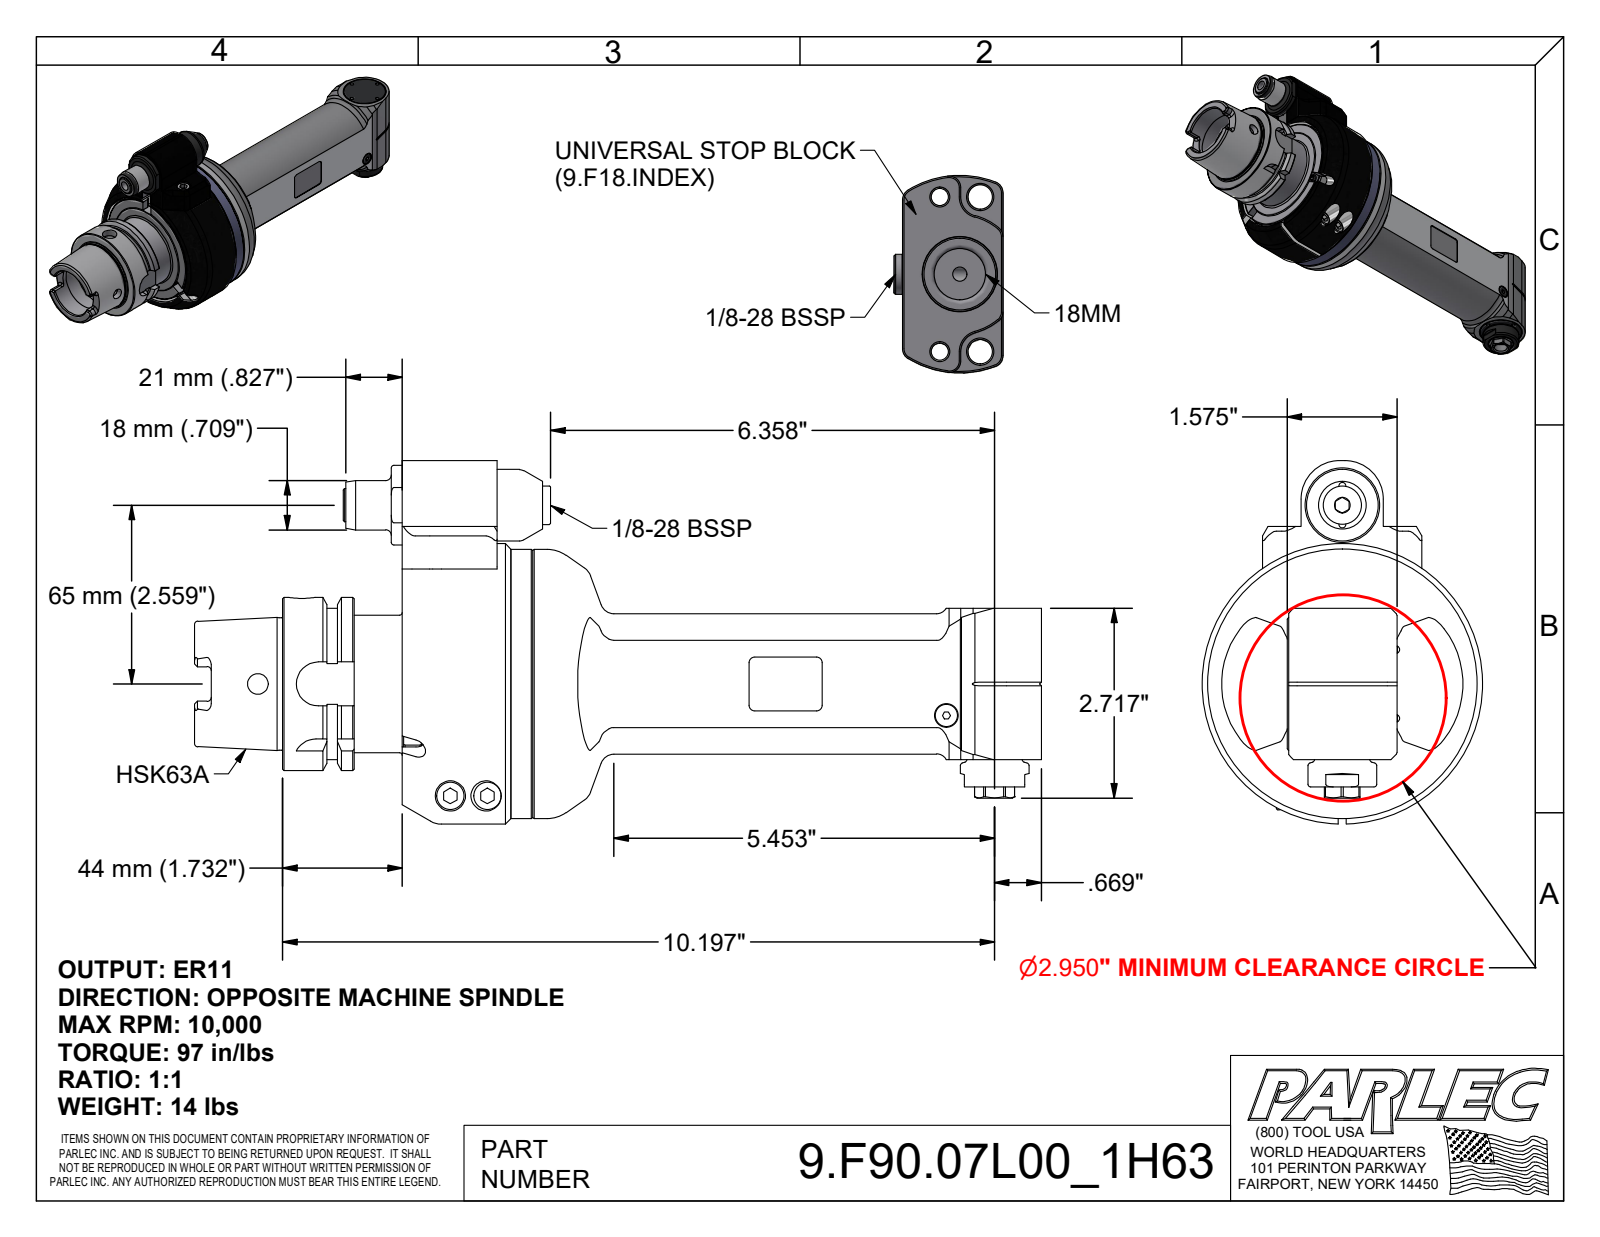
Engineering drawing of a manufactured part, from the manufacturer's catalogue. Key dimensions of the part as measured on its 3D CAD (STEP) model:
Part name (STEP PRODUCT): 9.F90.07L00-1H63; 9_GA1_566_2_1_H63; 9FL1ATC; 9HSK631ATC (+4 more)
STEP written by: Autodesk Inventor 2022 (AUTOMOTIVE_DESIGN)
Units: inches
Bodies: 5 solids, 557 faces (264 planar, 138 cylindrical, 155 other)
Overall size (bounding box): 12.126 × 5.206 × 4.016
Volume: 59.31 in³ · Surface area: 223.5 in²
Round holes (diameter × count): ⌀0.102 ×6, ⌀0.165 ×2, ⌀0.197 ×2, ⌀0.295 ×2, ⌀0.409 ×2, ⌀0.433 ×2, ⌀0.492 ×2, ⌀0.098 ×1, ⌀0.118 ×1, ⌀0.256 ×1, ⌀0.276 ×1, ⌀0.335 ×1
Round bosses / shafts (diameter × count): ⌀0.394 ×4, ⌀0.236 ×4, ⌀0.709 ×3, ⌀0.315 ×2, ⌀0.098 ×2, ⌀4.016 ×1, ⌀3.858 ×1, ⌀3.031 ×1
Partial cylindrical surfaces — rounded edges, fillets, slot ends (radius × count): R0.079 ×12, R0.059 ×6, R0.113 ×4, R0.157 ×4, R0.315 ×4, R0.016 ×2, R0.02 ×2, R0.039 ×2
Main face-to-face distances: 1.26, 1.575, 0.276, 1.024, 1.555, 0.02, 0.295, 0.197, 0.335, 0.984
Hole centre spacings: 0.492, 0.696, 0.276, 0.984, 9.933, 0.014, 0.478, 0.506
